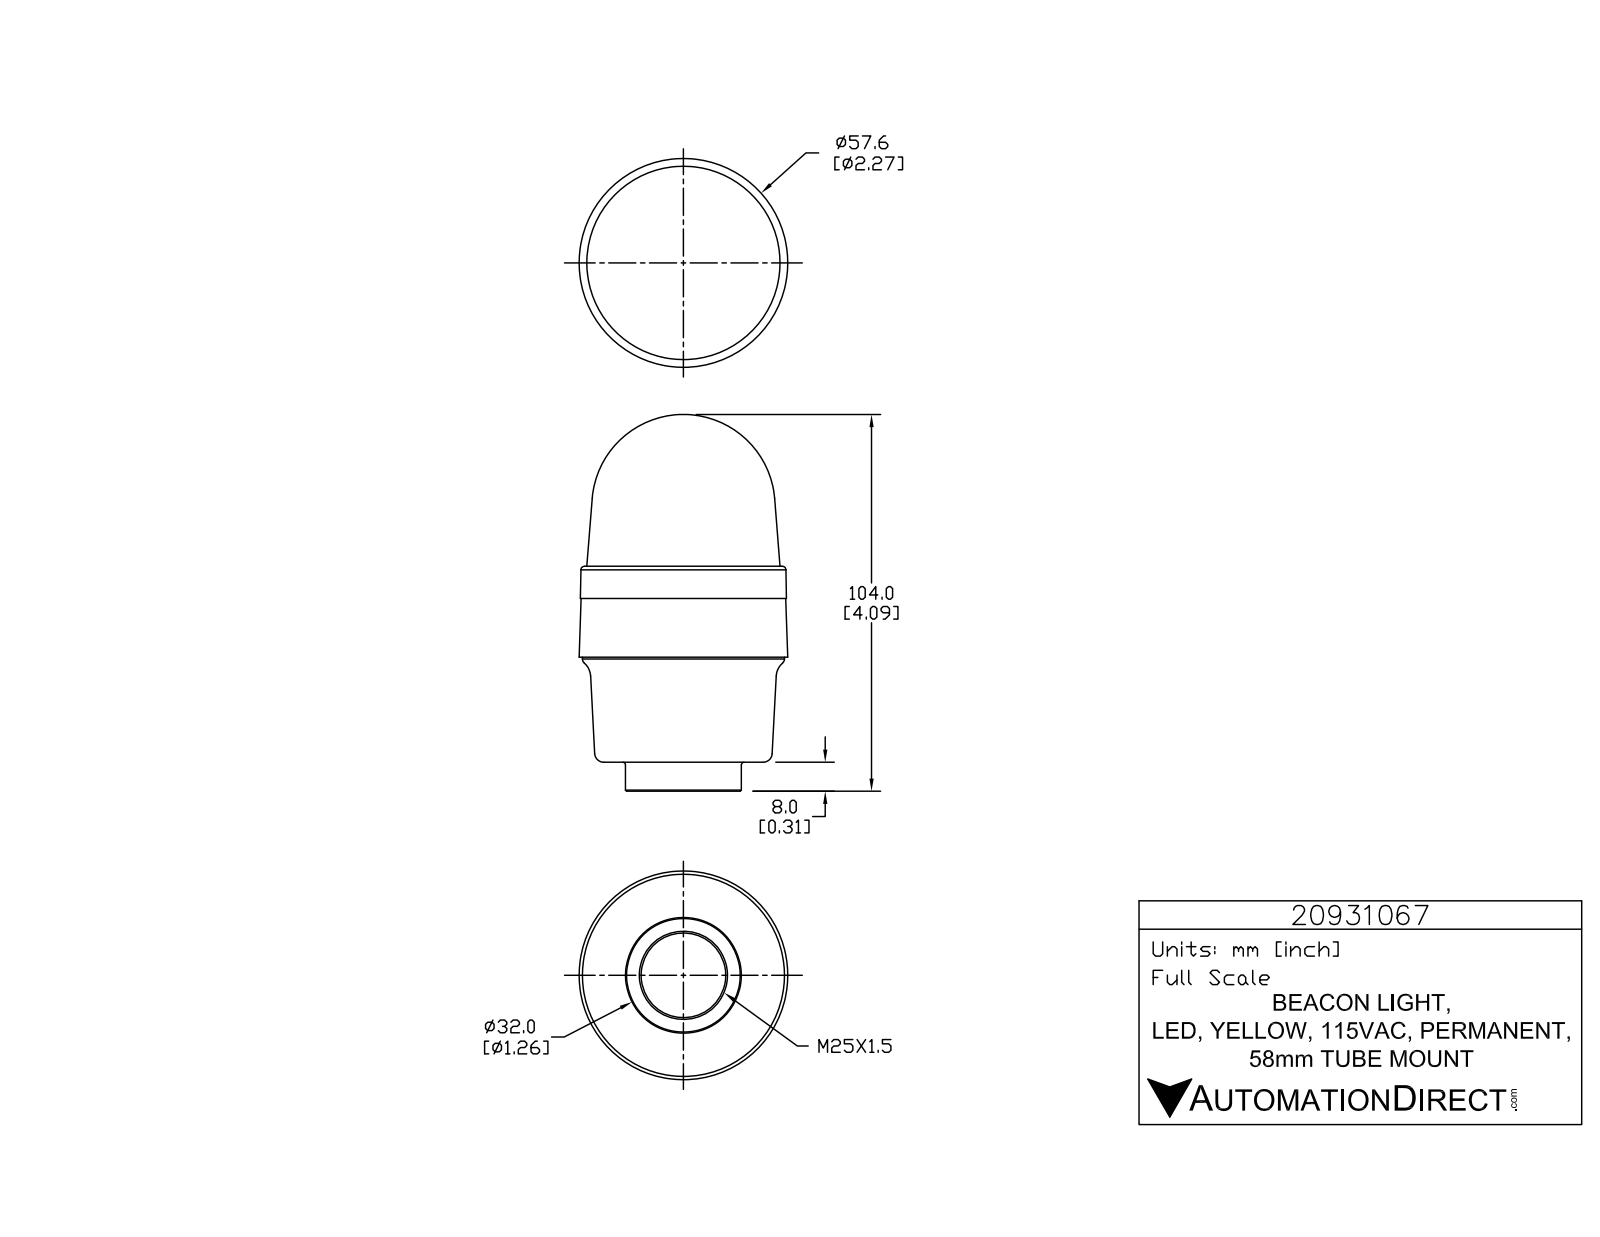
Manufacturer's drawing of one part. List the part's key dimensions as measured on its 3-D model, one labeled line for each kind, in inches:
Part name (STEP PRODUCT): 20931067
STEP written by: SolidWorks 2017 (AUTOMOTIVE_DESIGN)
Units: inches
Bodies: 1 solid, 791 faces (525 planar, 168 cylindrical, 98 other)
Overall size (bounding box): 4.051 × 2.269 × 2.269
Volume: 11.72 in³ · Surface area: 29.93 in²
Round holes (diameter × count): ⌀0.039 ×3, ⌀0.92 ×1
Round bosses / shafts (diameter × count): ⌀0.226 ×3, ⌀0.056 ×3, ⌀2.197 ×1, ⌀1.26 ×1
Partial cylindrical surfaces — rounded edges, fillets, slot ends (radius × count): R0.008 ×6, R0.008 ×6, R0.008 ×6, R0.131 ×6, R0.004 ×3, R0.005 ×3, R0.008 ×3, R0.008 ×3
Main face-to-face distances: 0.315, 1.142, 1.457, 0.988, 2.13, 2.445, 0.35, 0.638, 1.78, 2.094
